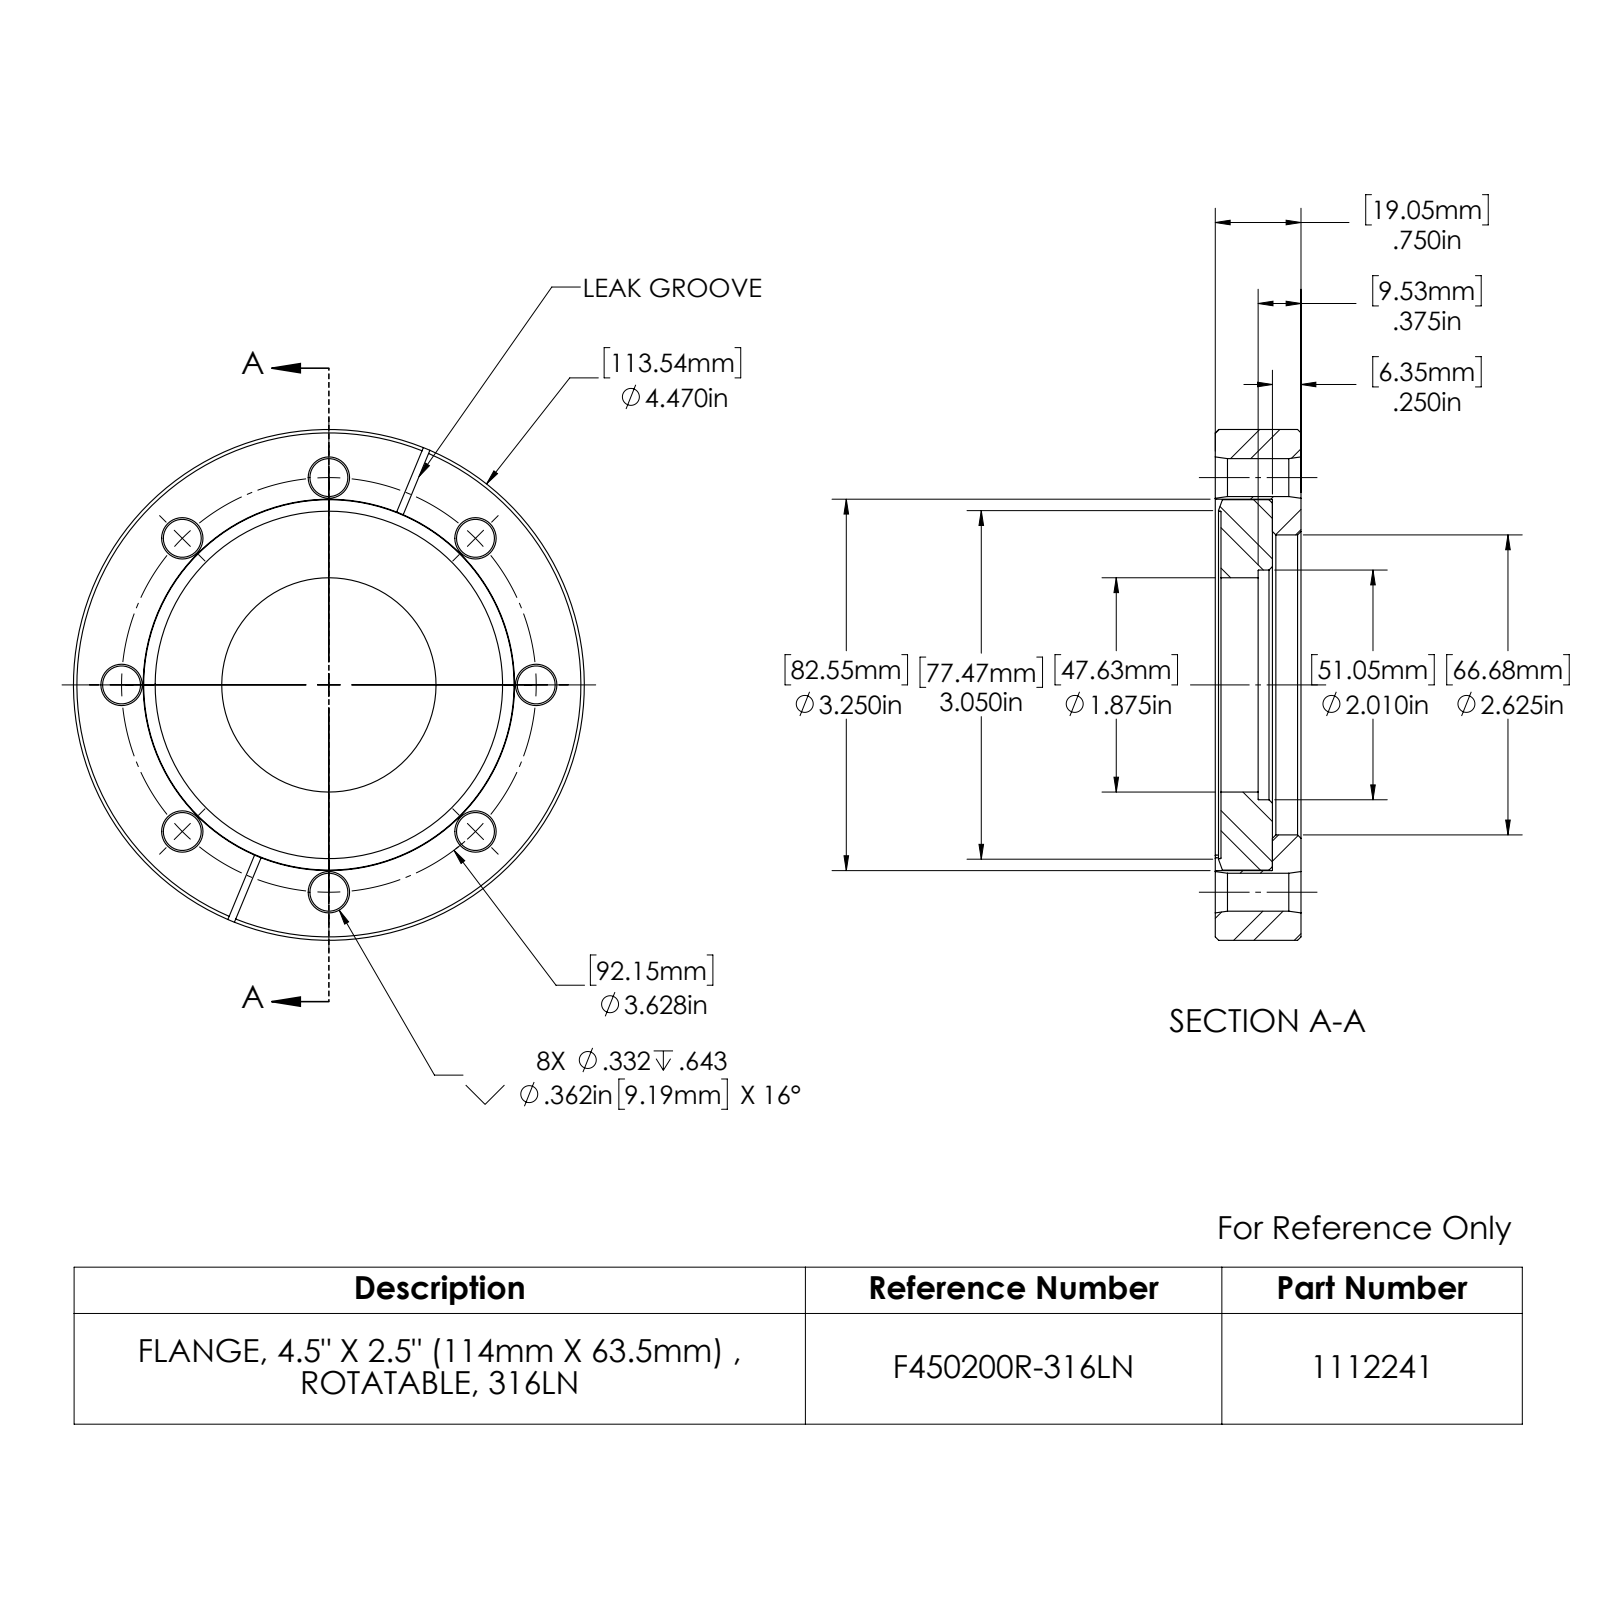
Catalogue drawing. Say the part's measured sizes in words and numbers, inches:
The part is named "1112241_A". Its 3-D file was written by "SolidWorks 2022 (CONFIG_CONTROL_DESIGN)". It is 2 solids with 101 faces: 13 planar, 30 cylindrical and 58 other. Overall it measures 4.47 by 4.47 by 0.75 inches. Its volume is 8.127 cubic inches and its surface area 60.34 square inches. Round holes: 8 of diameter 0.332, 1 of diameter 1.875, 1 of diameter 2.01, 1 of diameter 2.625, 1 of diameter 3.04, 1 of diameter 3.25. Round bosses or shafts: 1 of diameter 4.47, 1 of diameter 3.241. The main face-to-face distances are 0.25, 0.5, 0.75, 0.05, 0.45, 0.7, 0.375, 0.325, 0.125, 0.375. The hole center spacings are 1.814, 1.389, 2.565, 3.352, 3.628, 1.388, 2.566, 3.352.
